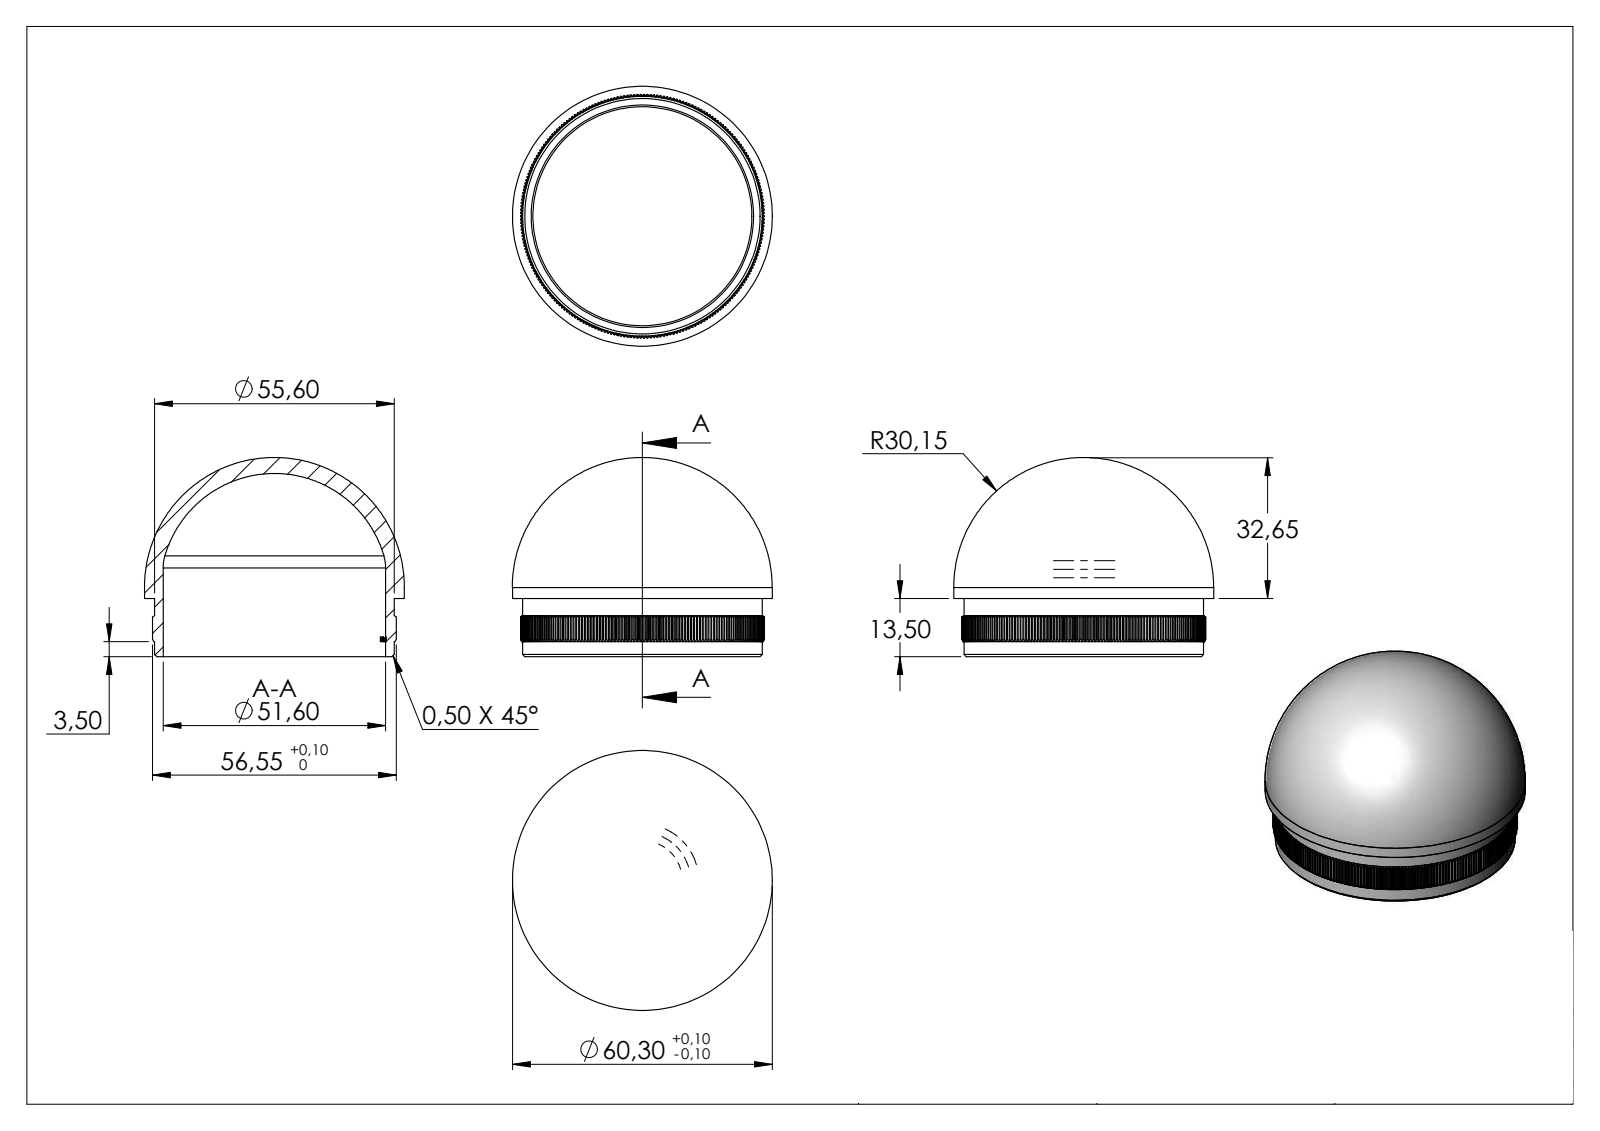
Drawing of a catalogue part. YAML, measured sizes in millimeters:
part_name: "50272-240G"
step_written_by: "SolidWorks 2018 (CONFIG_CONTROL_DESIGN)"
units: millimeters
bodies: {solids: 1, faces: 1620, planar: 797, cylindrical: 258, other: 565}
overall_size: [60.3, 60.3, 46.15]
volume: 25824
surface_area: 17031
round_holes:
  - {diameter: 51.6, count: 1}
round_bosses_or_shafts:
  - {diameter: 60.3, count: 1}
  - {diameter: 55.6, count: 1}
partial_cylinders:
  - {radius: 25.9, count: 1}
  - {radius: 28.27, count: 1}
face_to_face_distances: [27.58, 27.59, 13.5, 27.6, 27.57, 27.56, 3.5, 10, 27.54, 27.62]
